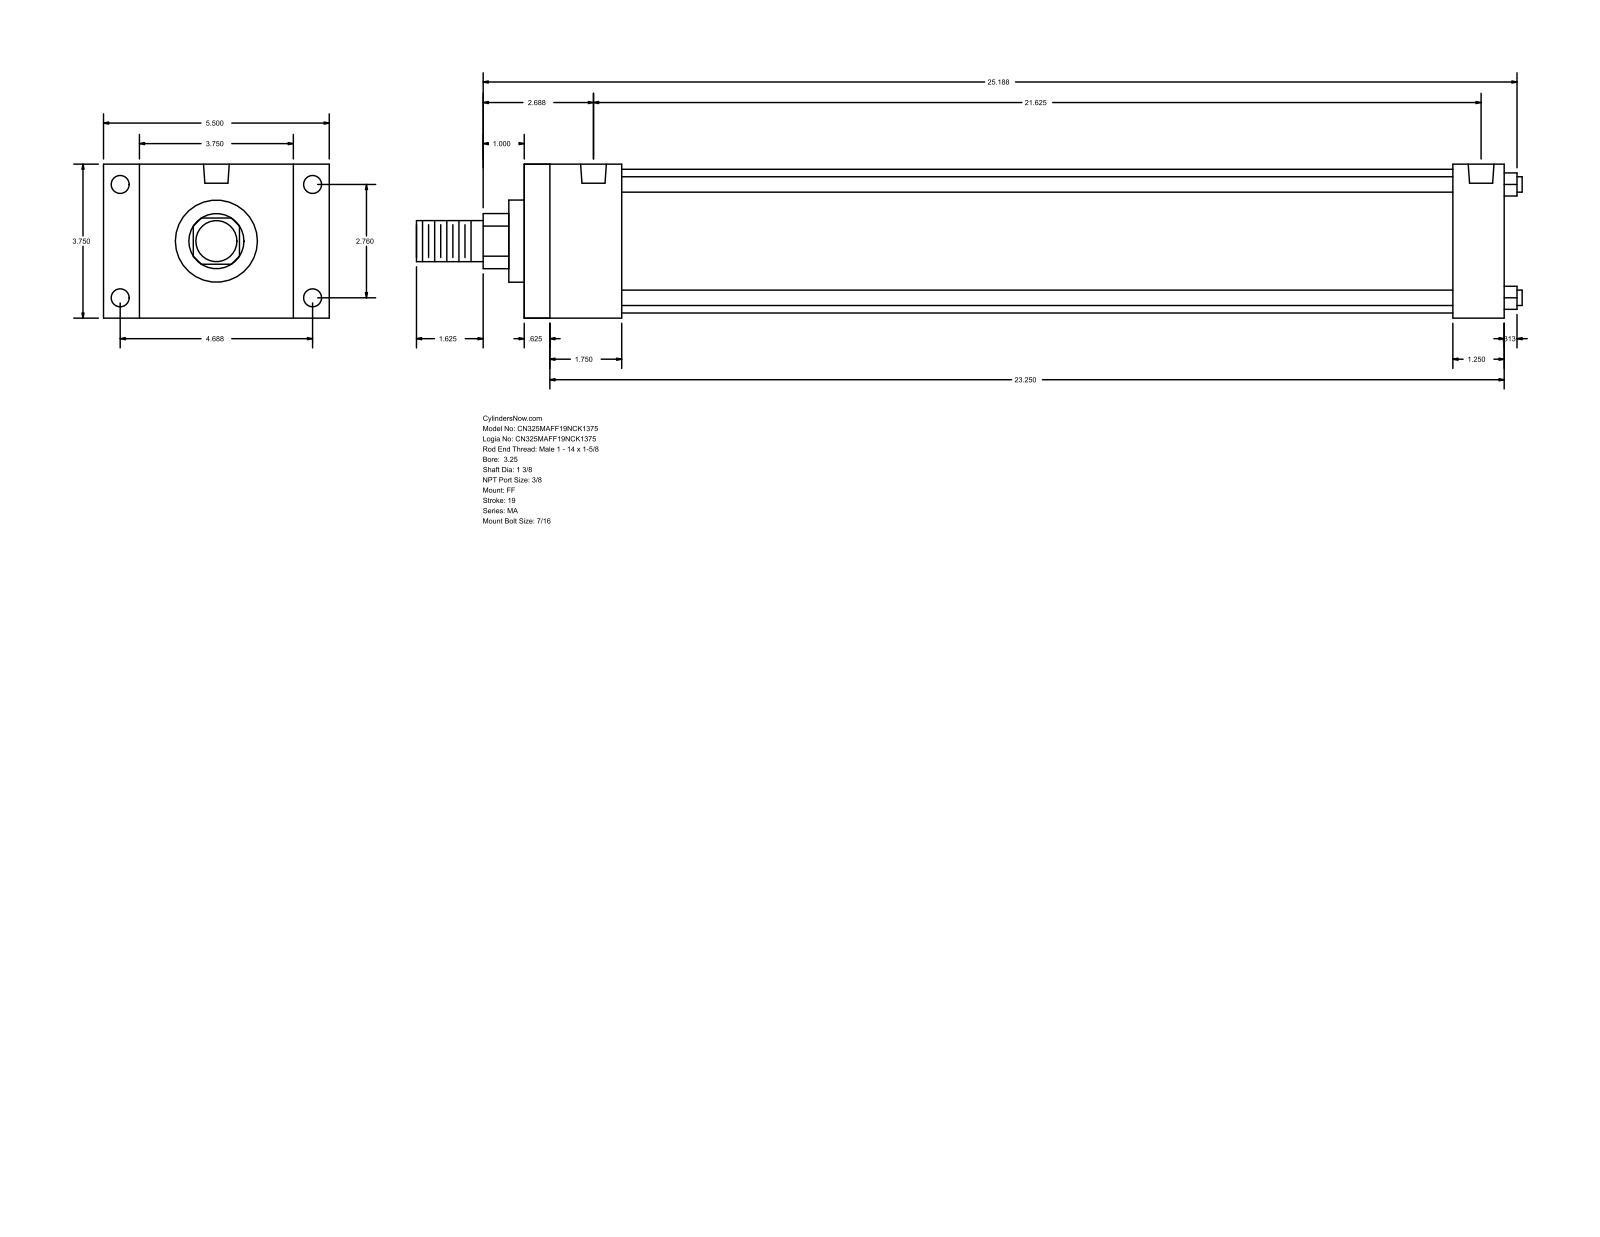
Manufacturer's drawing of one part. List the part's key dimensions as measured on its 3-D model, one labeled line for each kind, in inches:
Part name (STEP PRODUCT): MA_FF__0325_1.375
STEP written by: GSSL Pune (CONFIG_CONTROL_DESIGN)
Units: inches
Bodies: 0 solids, 92 faces (64 planar, 28 cylindrical, 0 other)
Overall size (bounding box): 26.937 × 5.5 × 3.75
Round holes (diameter × count): ⌀0.437 ×8, ⌀0.627 ×2
Round bosses / shafts (diameter × count): ⌀0.375 ×4, ⌀3.5 ×1, ⌀2 ×1, ⌀1.375 ×1, ⌀1 ×1
Partial cylindrical surfaces — rounded edges, fillets, slot ends (radius × count): R0.672 ×1
Main face-to-face distances: 3.75, 23.875, 0.625, 23.25, 0.875, 4.625, 2.375, 22.625, 1.75, 22
Hole centre spacings: 0.188, 2.76, 4.687, 5.439, 21.25, 21.437, 21.625
